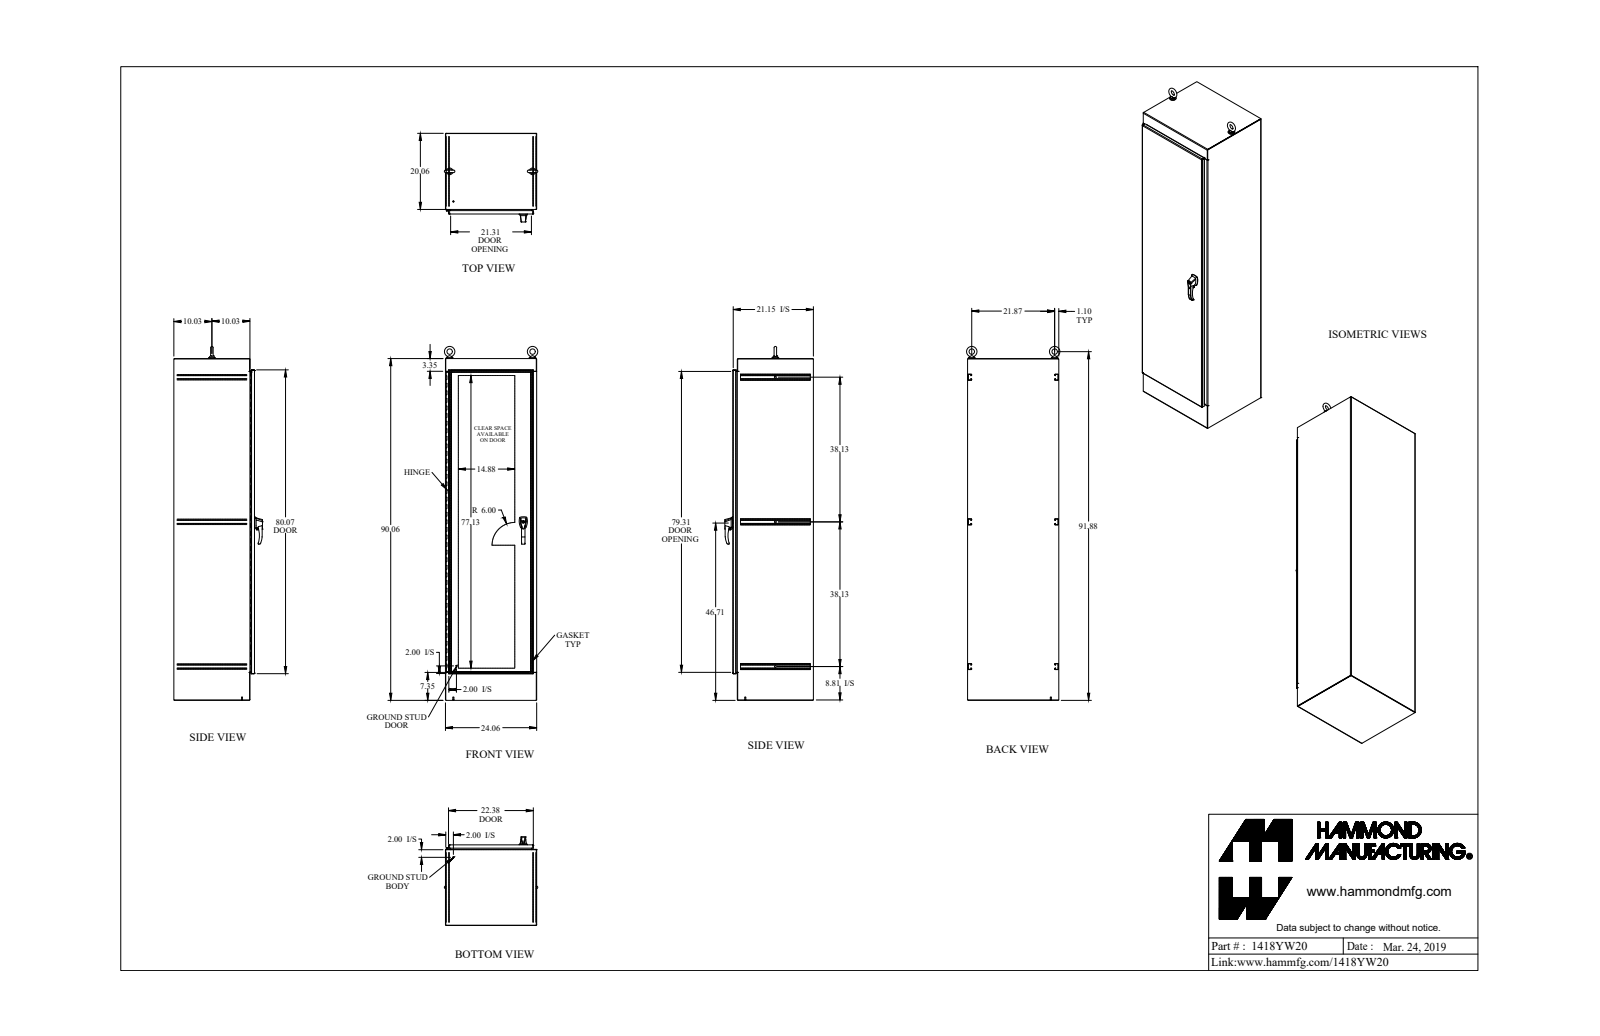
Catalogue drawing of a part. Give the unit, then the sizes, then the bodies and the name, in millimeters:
Units: millimetres
Overall size (bounding box): 2380.3 × 638 × 593.4
Round holes (diameter × count): ⌀7.7 ×14, ⌀19.1 ×4, ⌀12.7 ×3, ⌀6.4 ×2, ⌀6.5 ×2, ⌀7.1 ×2, ⌀7.1 ×2, ⌀8 ×2, ⌀9.9 ×2, ⌀10.5 ×2, ⌀13.4 ×2, ⌀15.9 ×2
Round bosses / shafts (diameter × count): ⌀7.1 ×4, ⌀44.5 ×2, ⌀38.1 ×2, ⌀31.8 ×2, ⌀25.4 ×2, ⌀19.1 ×2, ⌀18.7 ×2, ⌀16 ×2
Partial cylindrical surfaces — rounded edges, fillets, slot ends (radius × count): R1.1 ×42, R3.5 ×36, R3.2 ×22, R0.5 ×16, R1.2 ×14, R3.6 ×14, R1.5 ×10, R0.4 ×6
Main face-to-face distances: 2.4, 608.7, 2.4, 606.3, 534.8, 537.3, 611.1, 537.3, 539.7, 2285.1
Hole centre spacings: 152.4, 304.8, 457.2, 609.6, 762, 914.4, 1066.8, 1219.2
Volume: 16 570 000 mm³ · Surface area: 13 770 000 mm²
Bodies: 52 solids, 2632 faces (1124 planar, 1343 cylindrical, 165 other)
Part name (STEP PRODUCT): 1418YW20_Default
STEP written by: SolidWorks 2019 (CONFIG_CONTROL_DESIGN)
